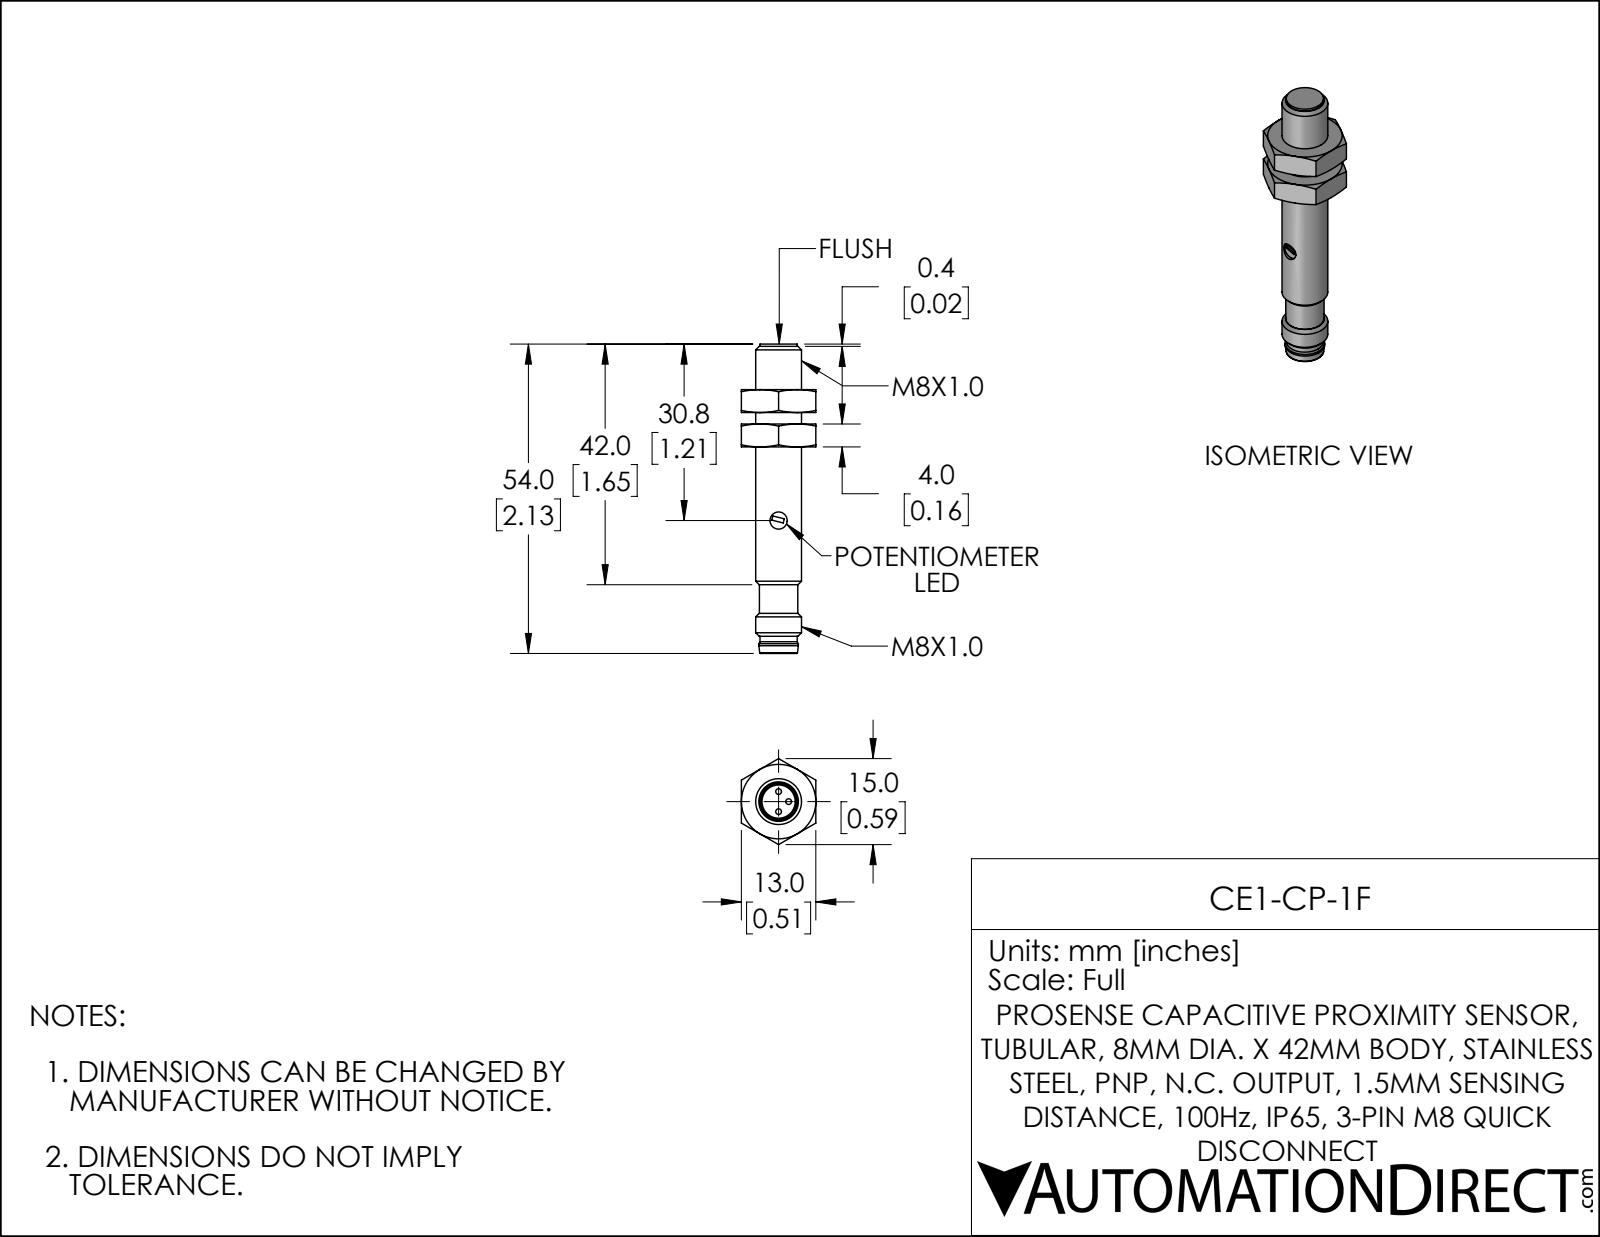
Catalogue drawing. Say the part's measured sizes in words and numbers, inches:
The part is named "CE1-CP-1F". Its 3-D file was written by "SolidWorks 2019 (CONFIG_CONTROL_DESIGN)". It is 3 solids with 80 faces: 31 planar, 13 cylindrical and 36 other. Overall it measures 2.126 by 0.591 by 0.512 inches. Its volume is 0.201 cubic inches and its surface area 3.838 square inches. Round holes: 1 of diameter 0.118, 1 of diameter 0.228, 1 of diameter 0.272. Round bosses or shafts: 3 of diameter 0.039, 1 of diameter 0.315, 1 of diameter 0.272, 1 of diameter 0.264, 1 of diameter 0.256. The main face-to-face distances are 0.512, 0.157, 0.236, 0.079, 0.394, 0.313, 0.47, 0.549, 0.707, 1.459.
